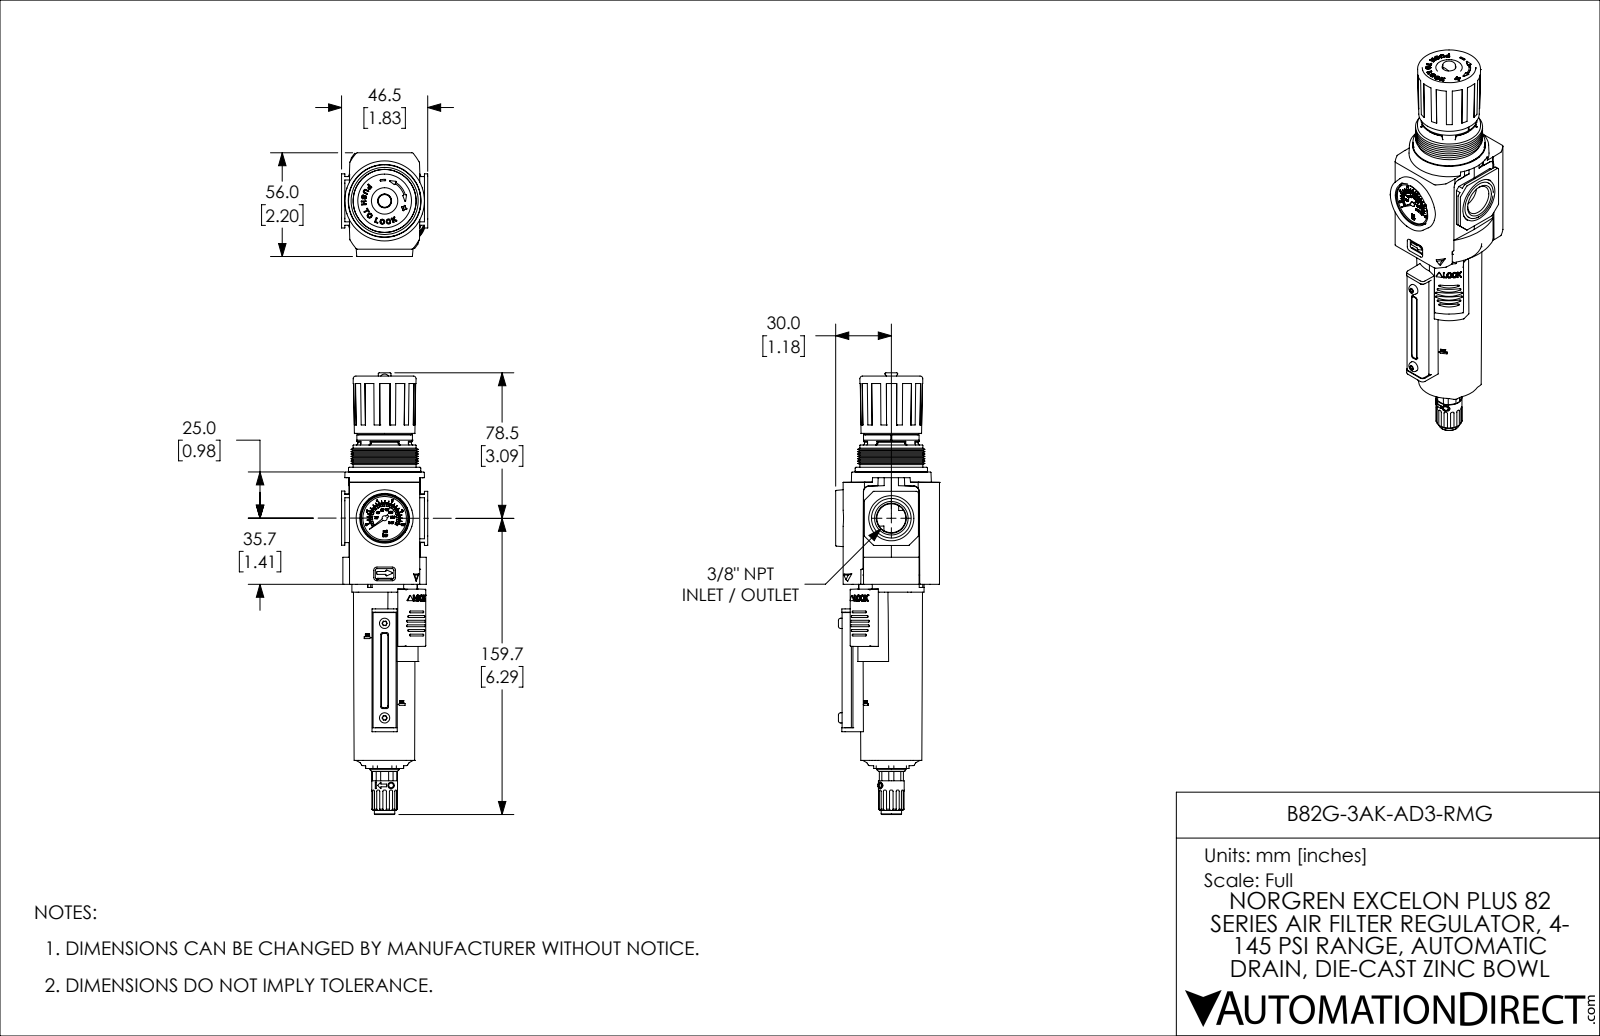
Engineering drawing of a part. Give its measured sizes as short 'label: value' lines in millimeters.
name: B82G-3AK-AD3-RMG
written by: SolidWorks 2021 (CONFIG_CONTROL_DESIGN)
unit: mm
bodies: 8 solids, 2693 faces (1022 planar, 1268 cylindrical, 403 other)
size: 238.2 × 56 × 46.5
volume: 275 300 mm³; area: 74 000 mm²
holes: 4× ⌀2.5, 2× ⌀3.5, 1× ⌀2.5, 1× ⌀3.3, 1× ⌀5, 1× ⌀6, 1× ⌀6.6, 1× ⌀16, 1× ⌀23.5, 1× ⌀28, 1× ⌀34.4
bosses: 2× ⌀5.7, 2× ⌀5.5, 2× ⌀3, 1× ⌀39, 1× ⌀35.3, 1× ⌀34.4, 1× ⌀34, 1× ⌀32.8
rounds: 50× R0.5, 50× R1, 25× R0.2, 20× R0.8, 19× R0.2, 13× R0.3, 12× R0.3, 12× R0.3
face distances: 1.5, 50.5, 43, 9, 41.5, 7.5, 36, 37.5, 4.6, 34.3
hole spacings: 16, 27.7, 32, 68.7, 84.5, 75.3, 136.5, 137.2
